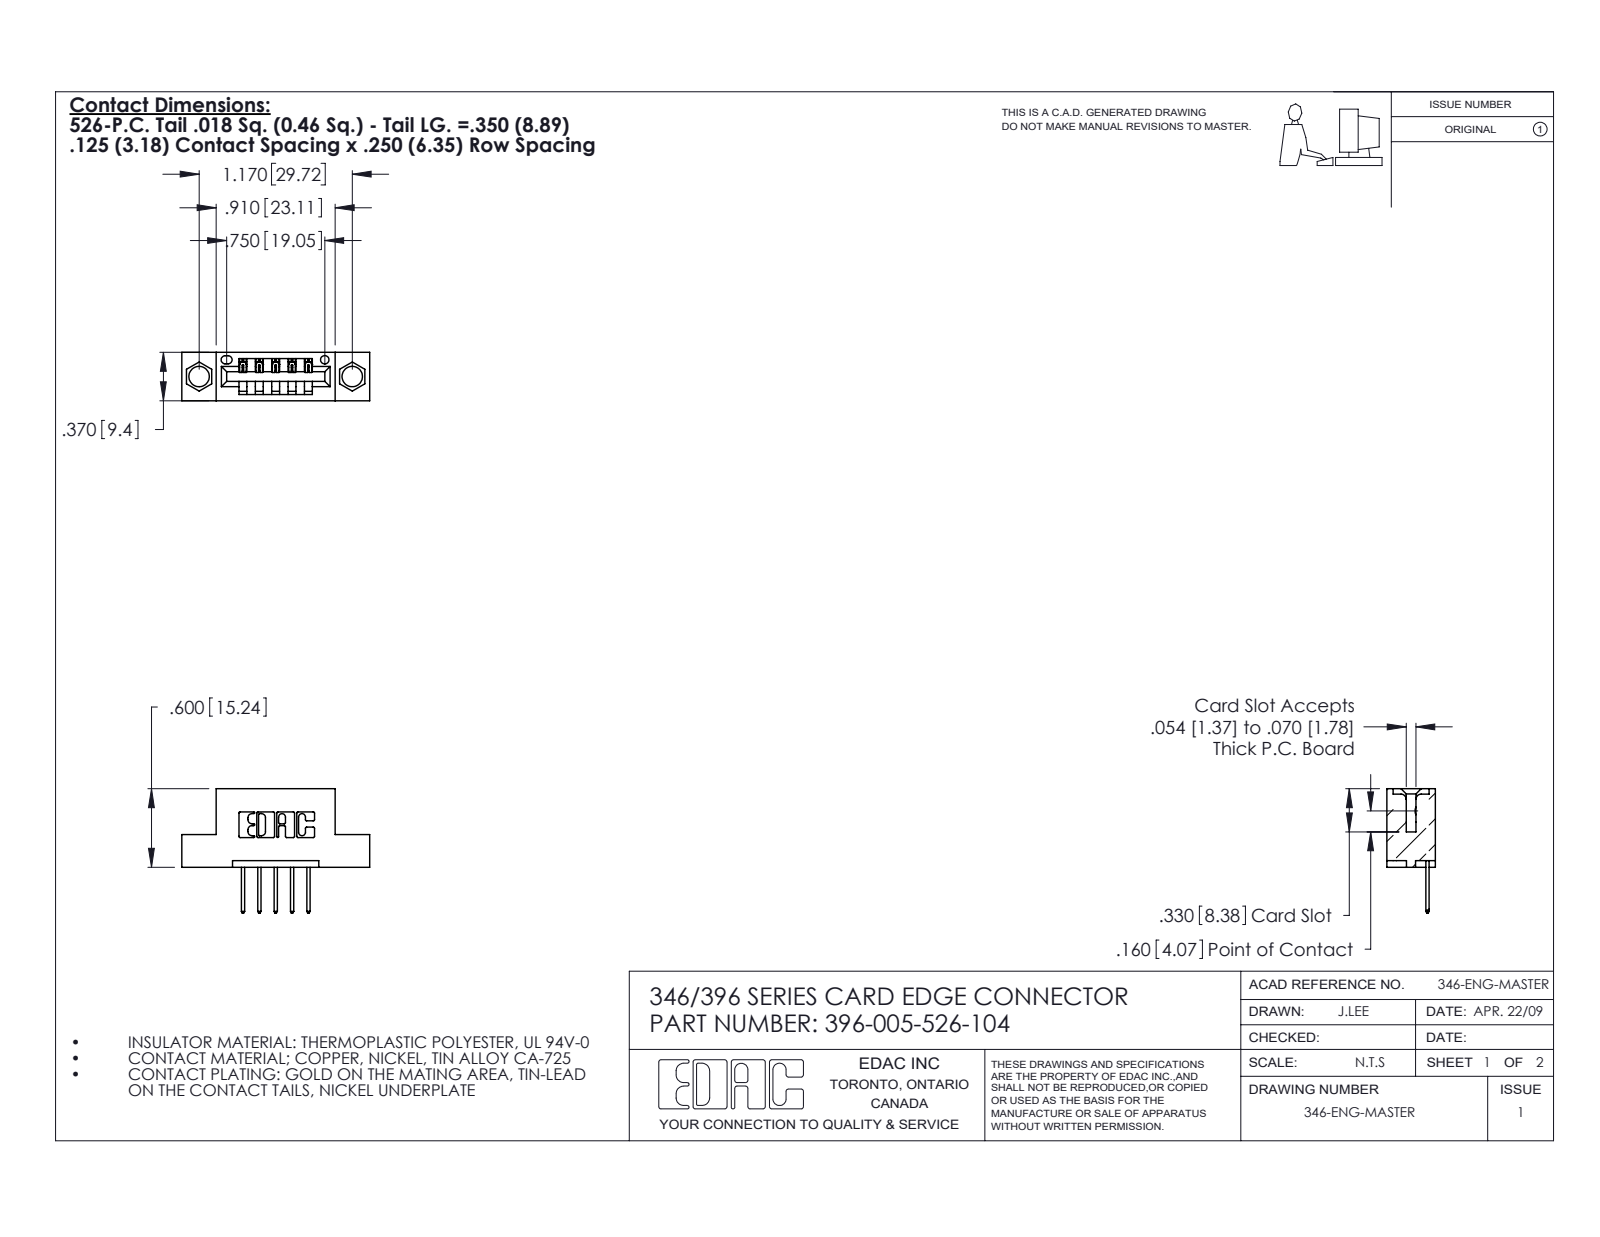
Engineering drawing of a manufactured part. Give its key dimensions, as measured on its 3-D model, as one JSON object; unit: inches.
{"part_name": "345-292-001_345-293-126; 346 Part_Flush Mounting Lugs - 0.156 Dia-TH; 396-005-526-104", "step_written_by": "SolidWorks 2020 (CONFIG_CONTROL_DESIGN)", "units": "inches", "bodies": {"solids": 6, "faces": 426, "planar": 290, "cylindrical": 136, "other": 0}, "overall_size": [1.435, 0.95, 0.37], "volume_in3": 0.191, "surface_area_in2": 5.174, "round_holes": [[0.156, 2], [0.064, 1]], "partial_cylinders_radius": [[0.01, 22], [0.006, 10], [0.01, 10], [0.007, 6], [0.031, 6], [0.026, 3], [0.031, 2], [0.04, 2]], "face_to_face_distances": [0.25, 0.37, 0.048, 0.322, 0.148, 0.222, 0.1, 0.174, 0.55, 0.125], "hole_center_spacings": [0.246, 0.969, 1.17]}
